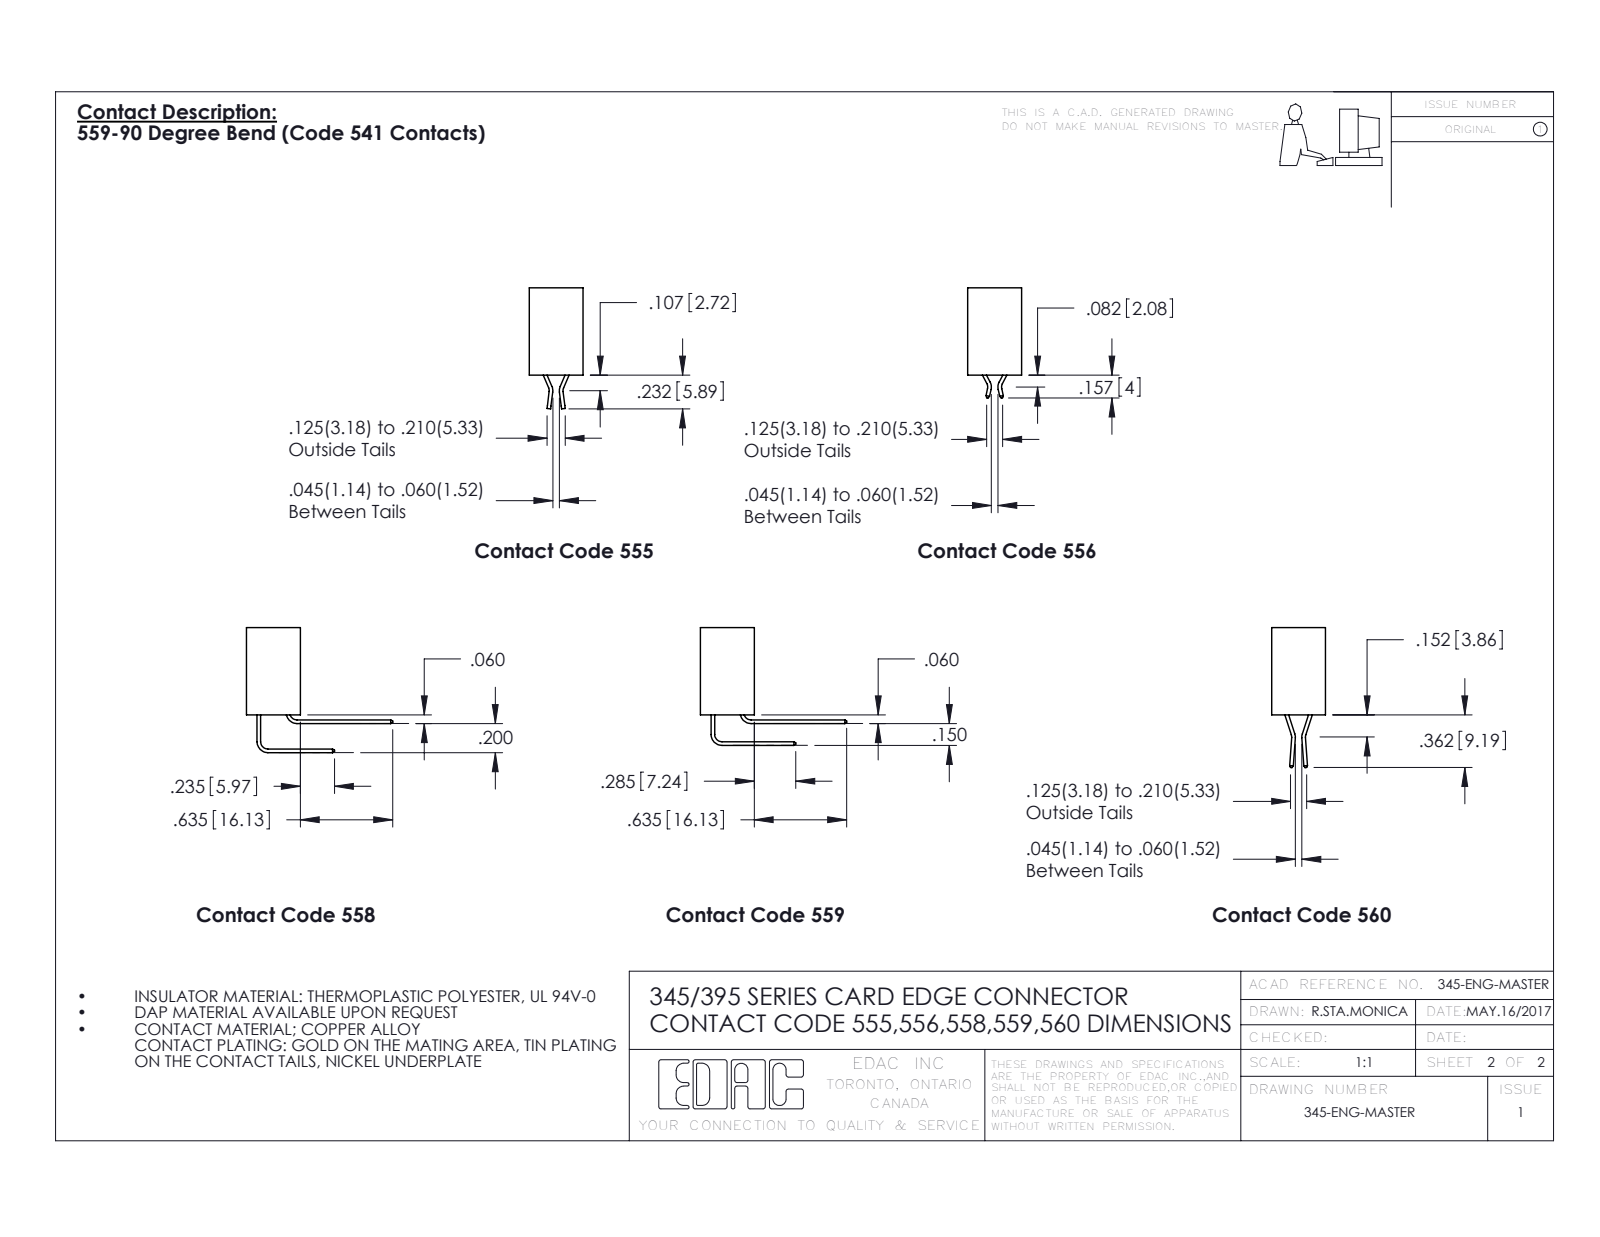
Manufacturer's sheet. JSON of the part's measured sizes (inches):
{"part_name": "345 Part_No Mounting Lugs; 345-292-001_345-293-124; 395-016-524-201", "step_written_by": "SolidWorks 2016 (CONFIG_CONTROL_DESIGN)", "units": "inches", "bodies": {"solids": 17, "faces": 982, "planar": 700, "cylindrical": 282, "other": 0}, "overall_size": [1.06, 0.762, 0.37], "volume_in3": 0.176, "surface_area_in2": 5.975, "round_holes": [[0.064, 1]], "partial_cylinders_radius": [[0.006, 24], [0.01, 22], [0.007, 6], [0.031, 6], [0.026, 3], [0.014, 2], [0.019, 2], [0.022, 2]], "face_to_face_distances": [0.2, 0.298, 0.072, 0.1, 0.37, 0.3, 0.098, 0.272, 0.025, 0.06]}
